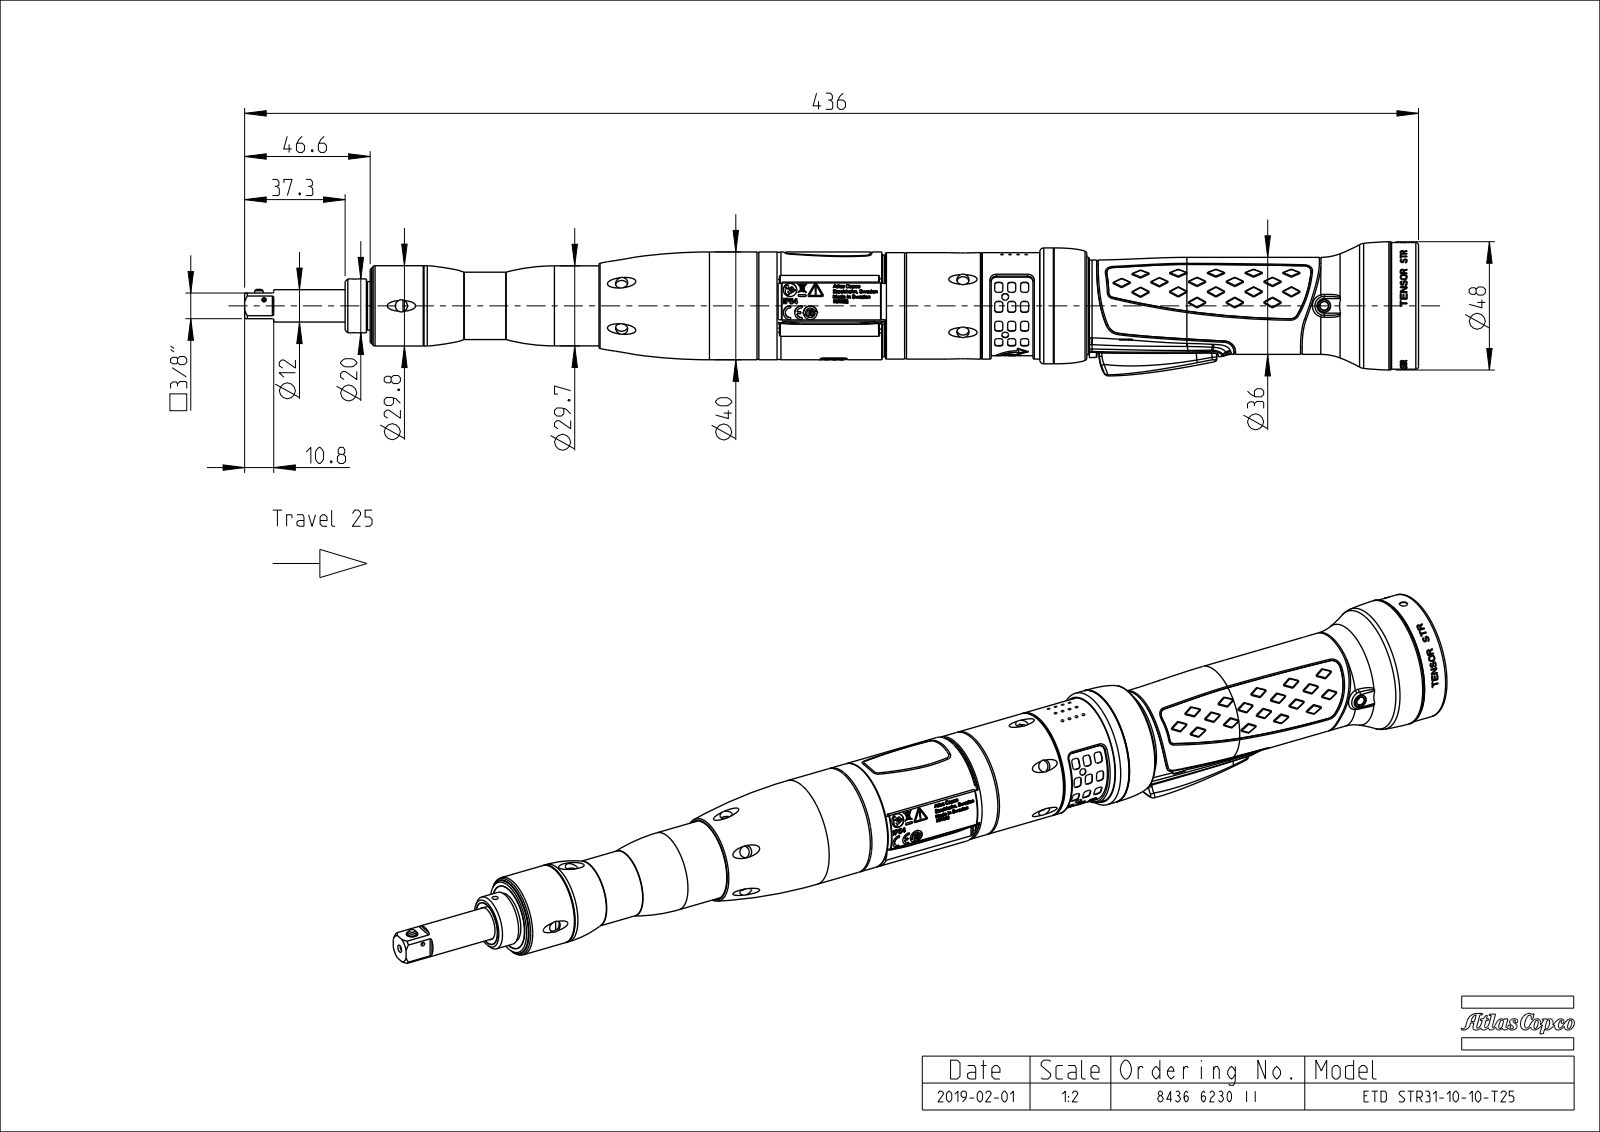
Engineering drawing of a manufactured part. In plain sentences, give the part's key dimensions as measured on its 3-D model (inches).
The part is named "4220474000; 4220447600; 4220125604; 4220473985_ASM (+8 more)". Its 3-D file was written by "CREO PARAMETRIC BY PTC INC, 2018100 (CONFIG_CONTROL_DESIGN)". It is 31 solids with 7051 faces: 2896 planar, 1168 cylindrical and 2987 other. Overall it measures 17.157 by 1.961 by 1.875 inches. Its volume is 8.249 cubic inches and its surface area 227.2 square inches. Round holes: 12 of diameter 0.039, 12 of diameter 0.105, 12 of diameter 0.13, 10 of diameter 0.142, 8 of diameter 0.177, 4 of diameter 0.102, 2 of diameter 0.063, 2 of diameter 0.126, 2 of diameter 0.197, 1 of diameter 0.015, 1 of diameter 0.028, 1 of diameter 0.059. Round bosses or shafts: 1 of diameter 1.85, 1 of diameter 1.732, 1 of diameter 1.693, 1 of diameter 1.575, 1 of diameter 1.559, 1 of diameter 1.555, 1 of diameter 1.551, 1 of diameter 1.476. Partial cylindrical surfaces (rounded edges, fillets, slot ends): 101 of radius 0.008, 74 of radius 0.02, 52 of radius 0.012, 19 of radius 0.079, 15 of radius 0.118, 11 of radius 0.028, 10 of radius 0.004, 10 of radius 0.059. The main face-to-face distances are 0.034, 1.261, 0.906, 5.478, 1.004, 0.098, 1.295, 1.227, 5.38, 3.906. The hole center spacings are 0.118, 0.236, 0.305, 0.176, 0.591, 0.835, 0.173, 0.354.
